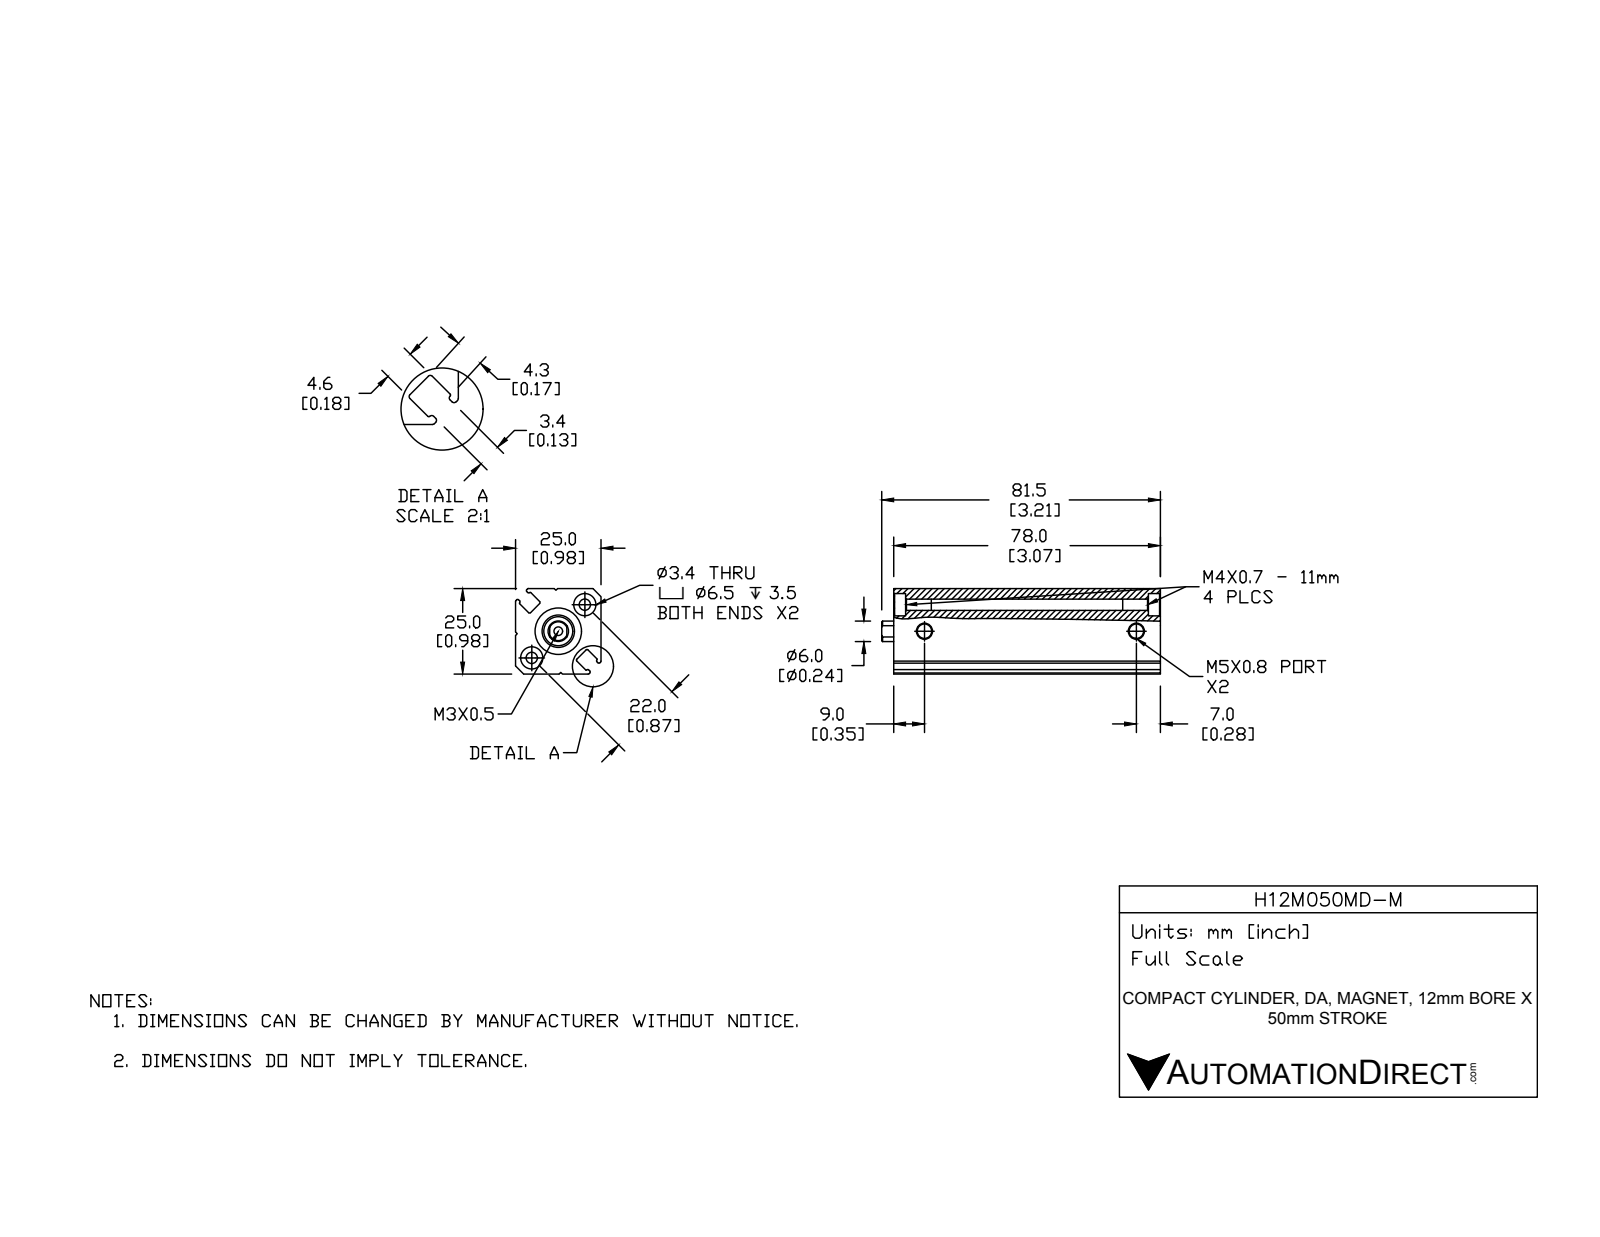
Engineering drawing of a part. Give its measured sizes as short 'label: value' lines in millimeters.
name: H12M050MD-M-BODY; H12M050MD-M-PISTON; H12M050MD-M
written by: SolidWorks 2015 (CONFIG_CONTROL_DESIGN)
unit: mm
bodies: 2 solids, 128 faces (49 planar, 54 cylindrical, 25 other)
size: 81.5 × 25 × 25
volume: 37 228 mm³; area: 17 020 mm²
holes: 2× ⌀3.3, 2× ⌀4.2, 2× ⌀6.5, 1× ⌀2.5, 1× ⌀6, 1× ⌀12, 1× ⌀13.6
bosses: 1× ⌀9.5
rounds: 16× R0.4, 4× R0.2
face distances: 25, 4.6, 13.7, 18.3, 78, 19.2, 5.5, 32, 72.5, 4
hole spacings: 11, 22.01, 62
